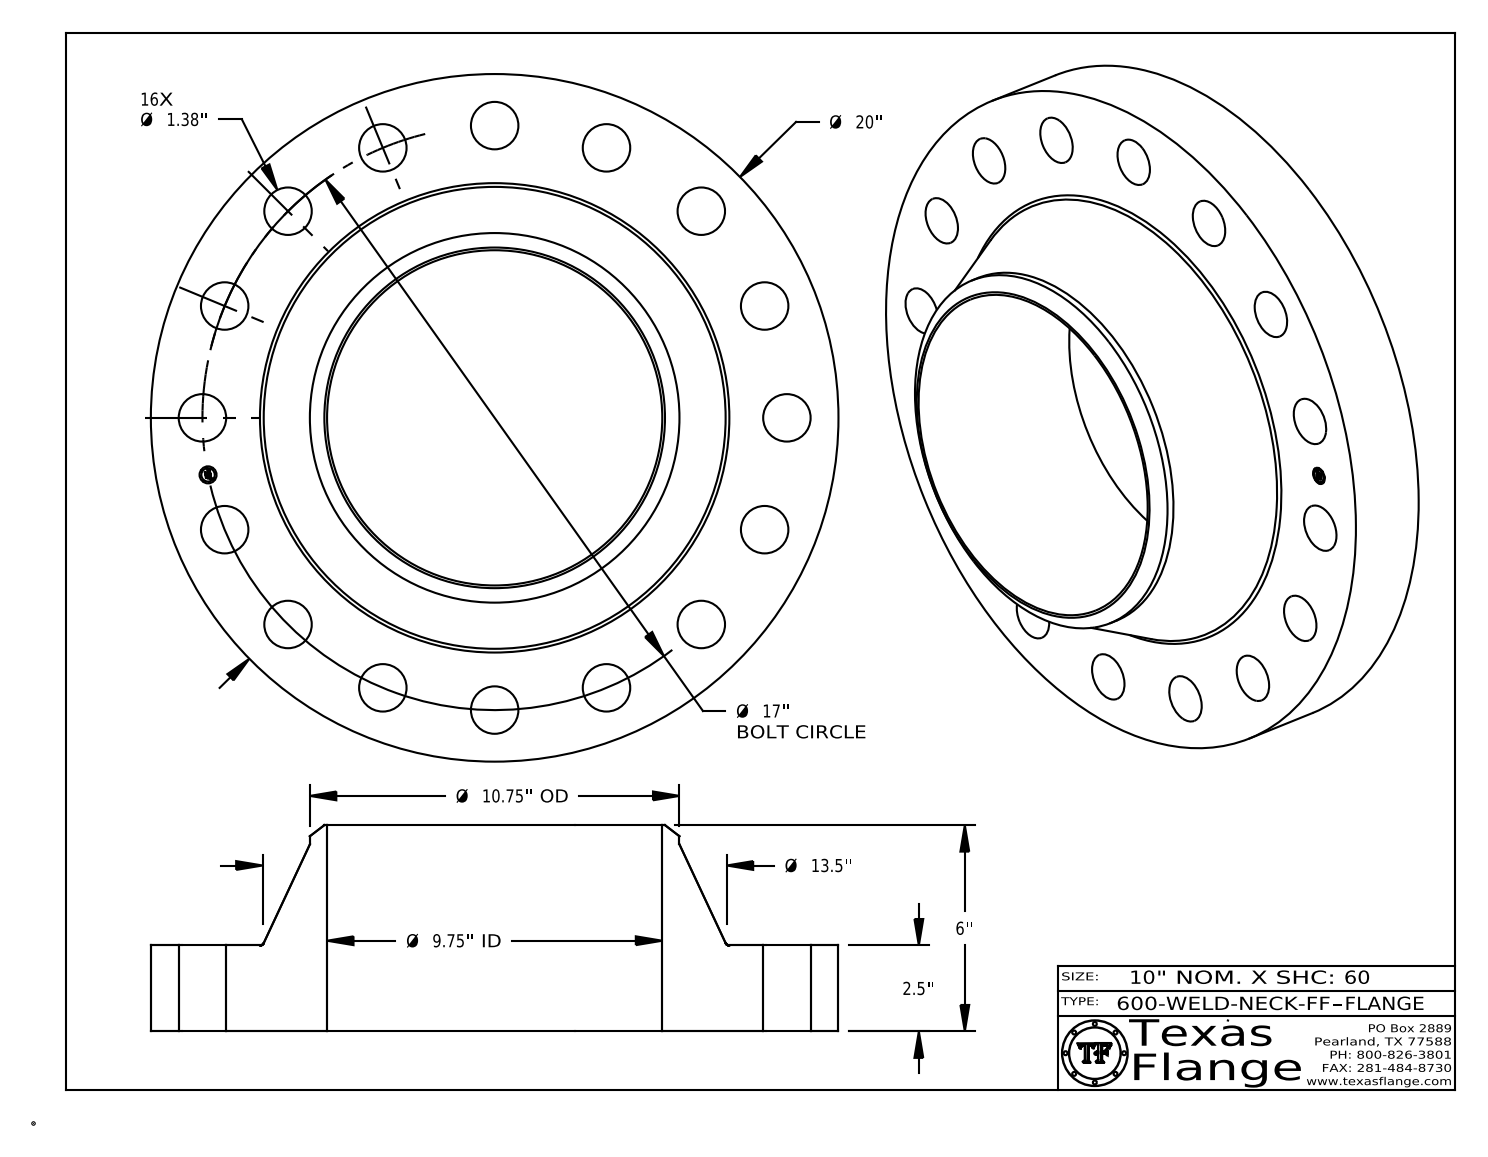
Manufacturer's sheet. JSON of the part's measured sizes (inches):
{"part_name": "600-WELD-NECK-FF", "step_written_by": "CATIA V5 STEP AP214 (AUTOMOTIVE_DESIGN)", "units": "inches", "bodies": {"solids": 1, "faces": 432, "planar": 368, "cylindrical": 58, "other": 6}, "overall_size": [20, 20, 6], "volume_in3": 667.2, "surface_area_in2": 1028, "round_holes": [[1.38, 16], [0.495, 1], [9.75, 1]], "round_bosses_or_shafts": [[0.03, 8], [20, 1], [10.75, 1], [0.39, 1]], "face_to_face_distances": [2.5, 6, 3.5, 2.485, 0.015, 3.515, 0.148, 0.145, 0.027, 0.096], "hole_center_spacings": [3.317, 14.135, 8.5, 6.506, 12.021, 9.444, 9.445, 15.706]}
